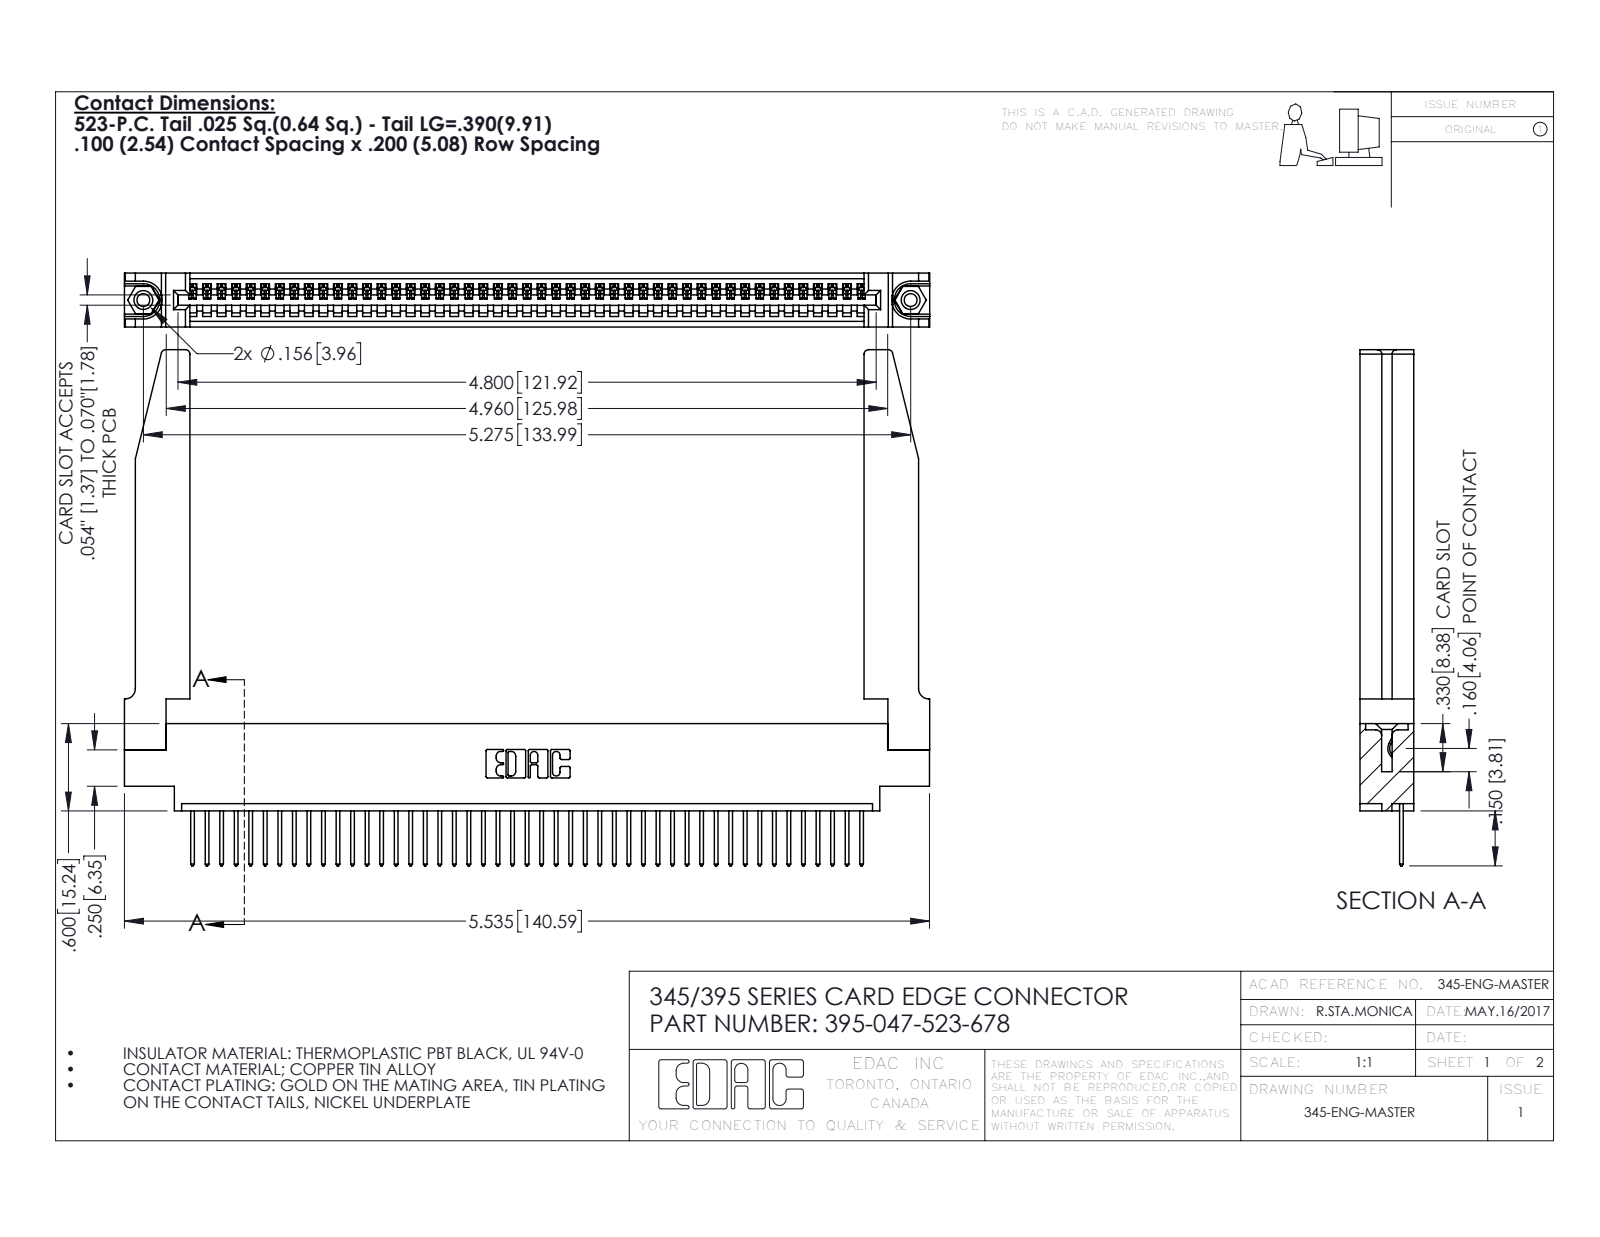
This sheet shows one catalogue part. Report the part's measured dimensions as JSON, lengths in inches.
{"part_name": "345-220-078_345-220-078; 395-047-523-678; 345-250-001_345-250-001-102; 345 Part_0.170 Offset - 0.156 Dia-TH (+1 more)", "step_written_by": "SolidWorks 2016 (CONFIG_CONTROL_DESIGN)", "units": "inches", "bodies": {"solids": 52, "faces": 3090, "planar": 2106, "cylindrical": 932, "other": 52}, "overall_size": [5.536, 3.547, 0.37], "volume_in3": 1.284, "surface_area_in2": 38.32, "round_holes": [[0.089, 2], [0.125, 2], [0.156, 2], [0.064, 1]], "round_bosses_or_shafts": [[0.155, 2]], "partial_cylinders_radius": [[0.006, 94], [0.01, 94], [0.01, 22], [0.03, 8], [0.007, 6], [0.031, 6], [0.026, 3], [0.031, 2]], "face_to_face_distances": [0.37, 0.072, 0.298, 0.098, 0.272, 0.025, 0.2, 0.225, 0.148, 0.15], "hole_center_spacings": [0.27, 5.039, 5.275]}
